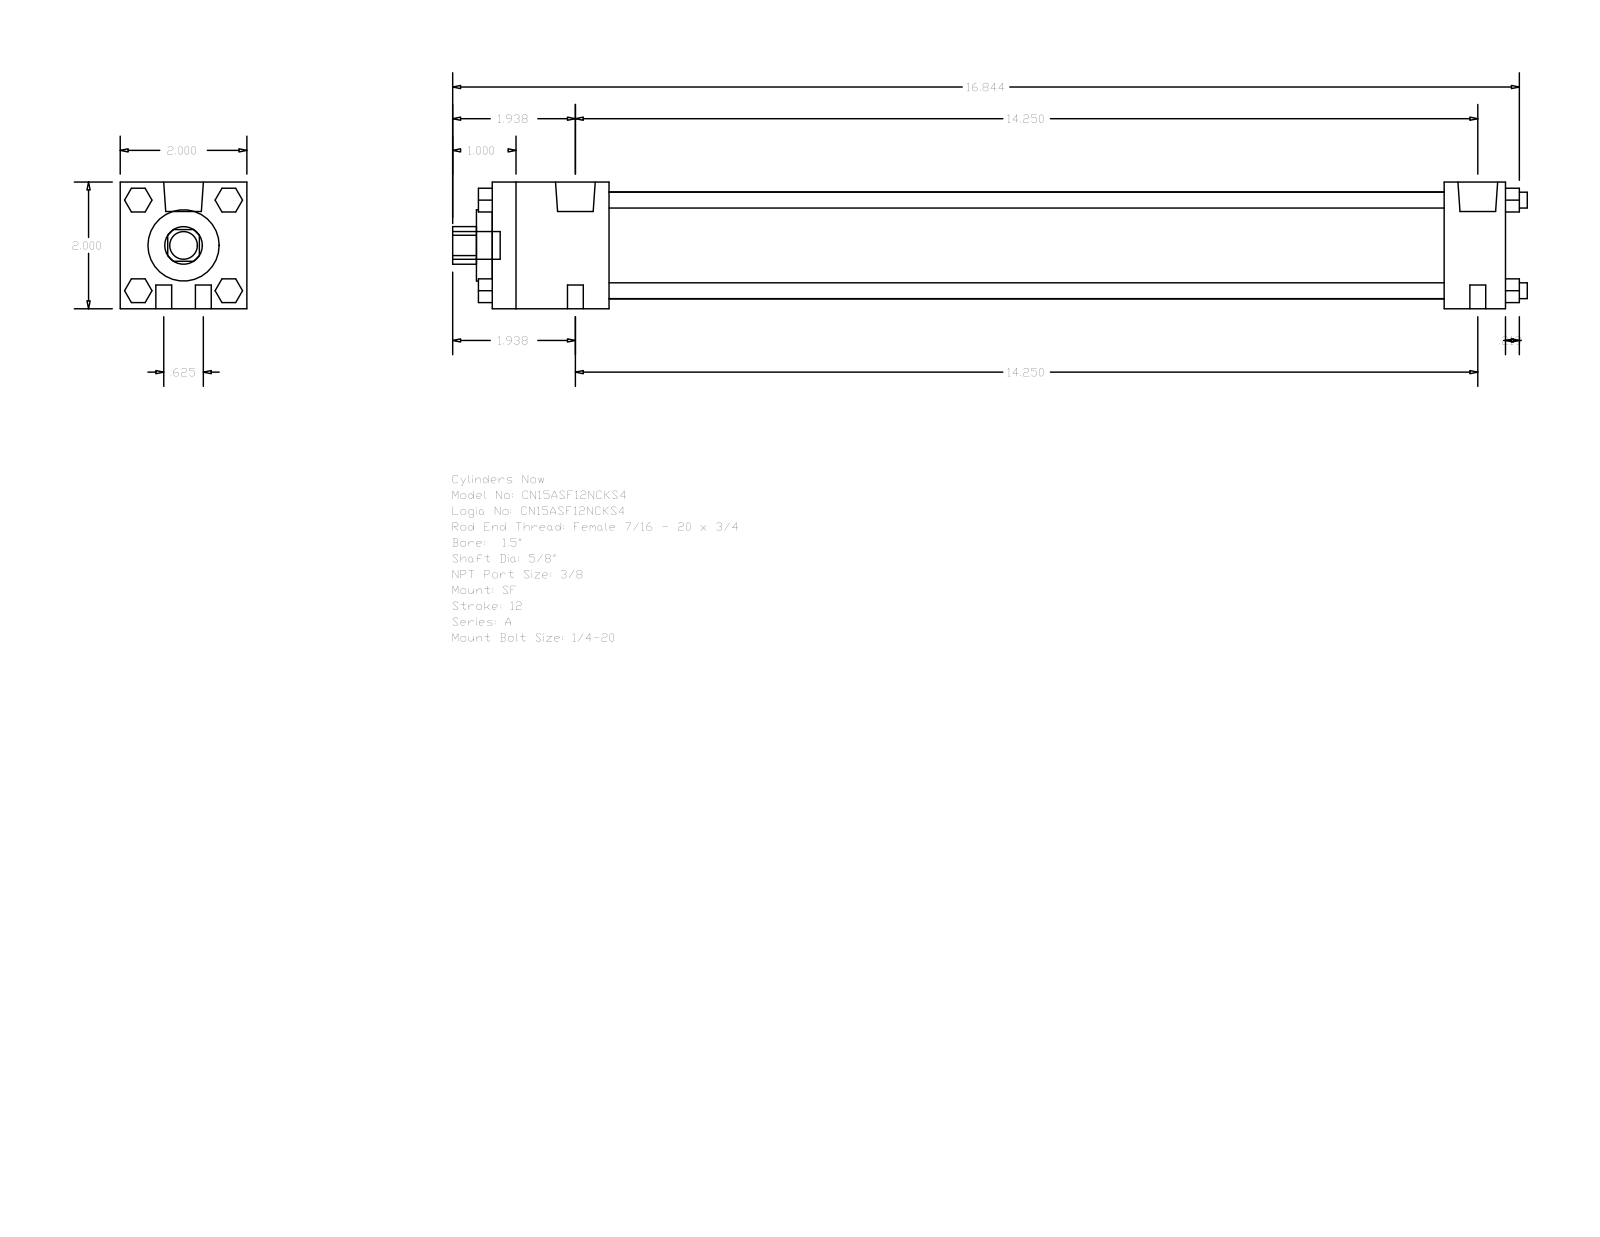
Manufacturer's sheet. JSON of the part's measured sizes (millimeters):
{"part_name": "A_SF__0150_0.625", "step_written_by": "GSSL Pune (CONFIG_CONTROL_DESIGN)", "units": "millimeters", "bodies": {"solids": 0, "faces": 124, "planar": 94, "cylindrical": 30, "other": 0}, "overall_size": [431.01, 50.8, 50.8], "round_holes": [[15.88, 1], [28.57, 1], [42.93, 1]], "round_bosses_or_shafts": [[6.35, 8], [15.93, 2], [5.56, 2], [11.11, 1]], "partial_cylinders_radius": [[7.54, 1]], "face_to_face_distances": [50.8, 406.39, 46.83, 381.79, 334.96, 359.56, 24.6, 9.52, 6.35, 53.18]}
